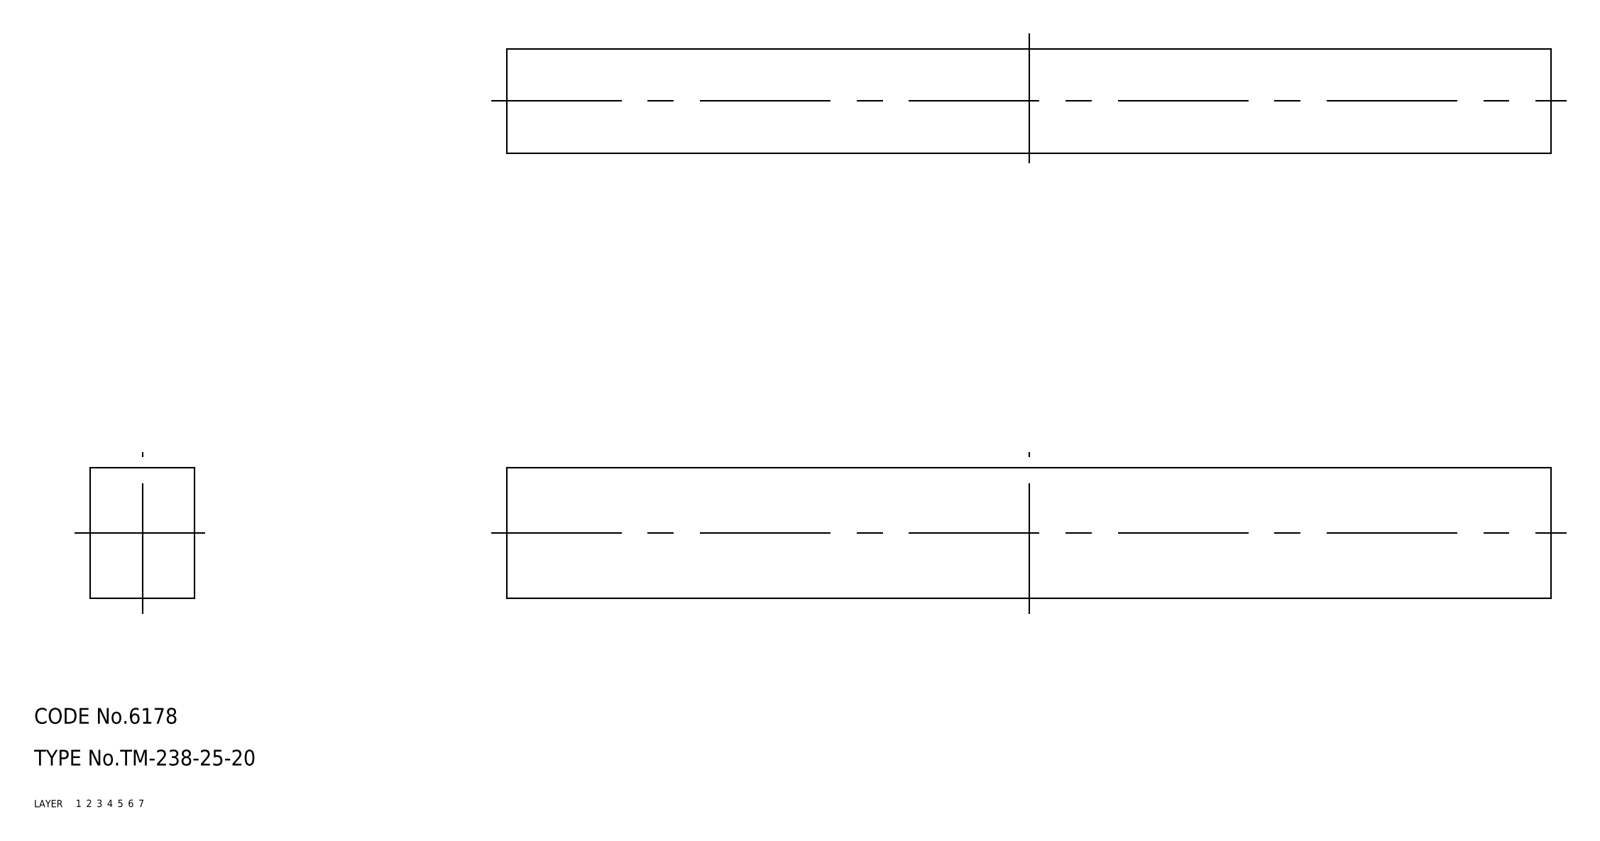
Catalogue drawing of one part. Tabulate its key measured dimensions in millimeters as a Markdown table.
| quantity | value |
| --- | --- |
| part name | rubber foam |
| STEP written by | CADfix (AUTOMOTIVE_DESIGN) |
| units | millimeters |
| bodies | 1 solid, 6 faces (0 planar, 0 cylindrical, 6 other) |
| overall size | 200 × 25 × 20 |
| volume | 100 000 mm³ |
| surface area | 19 000 mm² |
